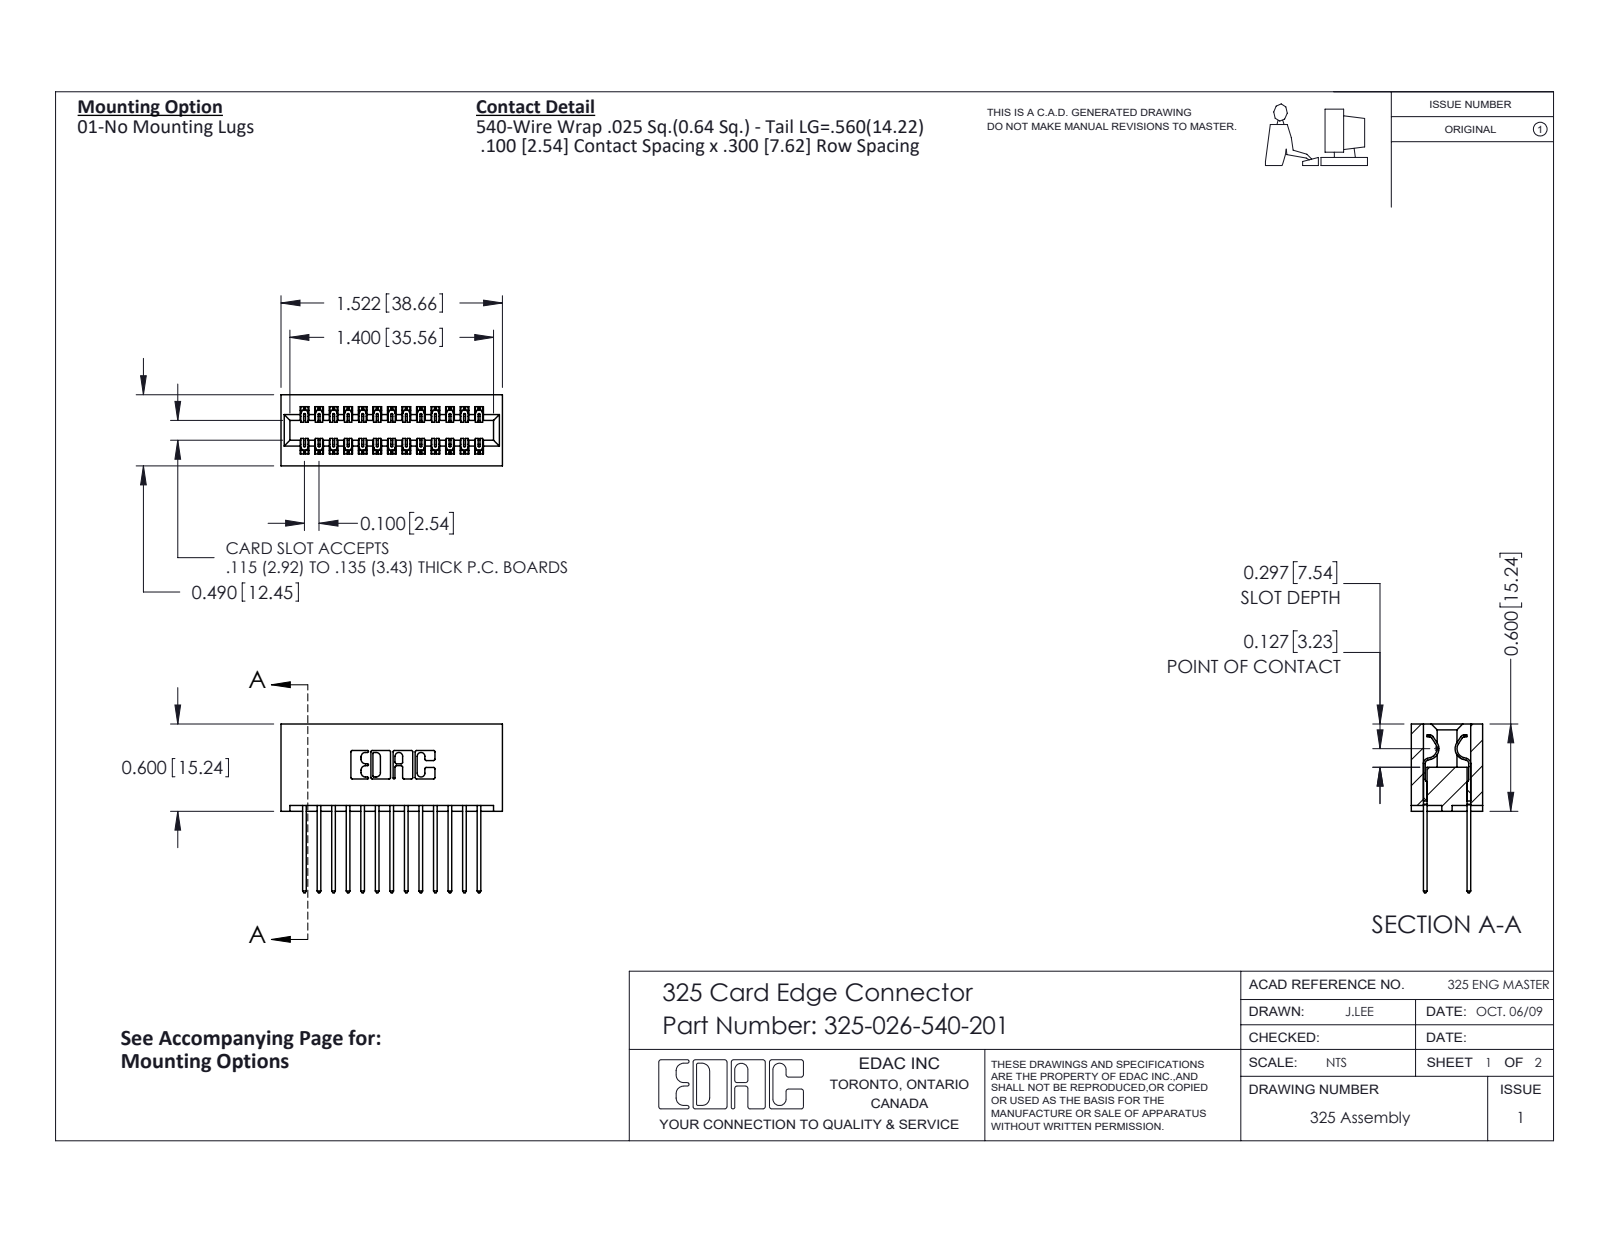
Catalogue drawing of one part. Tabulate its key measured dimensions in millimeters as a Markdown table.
| quantity | value |
| --- | --- |
| part name | 325-026-540-201; 325 Part_Lugless; 325-292-001_325-293-140 |
| STEP written by | SolidWorks 2016 (CONFIG_CONTROL_DESIGN) |
| units | millimeters |
| bodies | 27 solids, 1458 faces (1002 planar, 456 cylindrical, 0 other) |
| overall size | 38.7 × 29.5 × 12.4 |
| volume | 5 440 mm³ |
| surface area | 7 019 mm² |
| partial cylindrical surfaces (radius × count) | 0.2 × 39, 0.3 × 26, 0.3 × 22, 0.2 × 6, 0.8 × 6, 0.7 × 3, 0.4 × 2, 0.6 × 2 |
| main face-to-face distances | 2.1, 10.3, 7.6, 2.7, 9.7, 0.6, 2.5, 8.3, 12.4, 5.1 |
